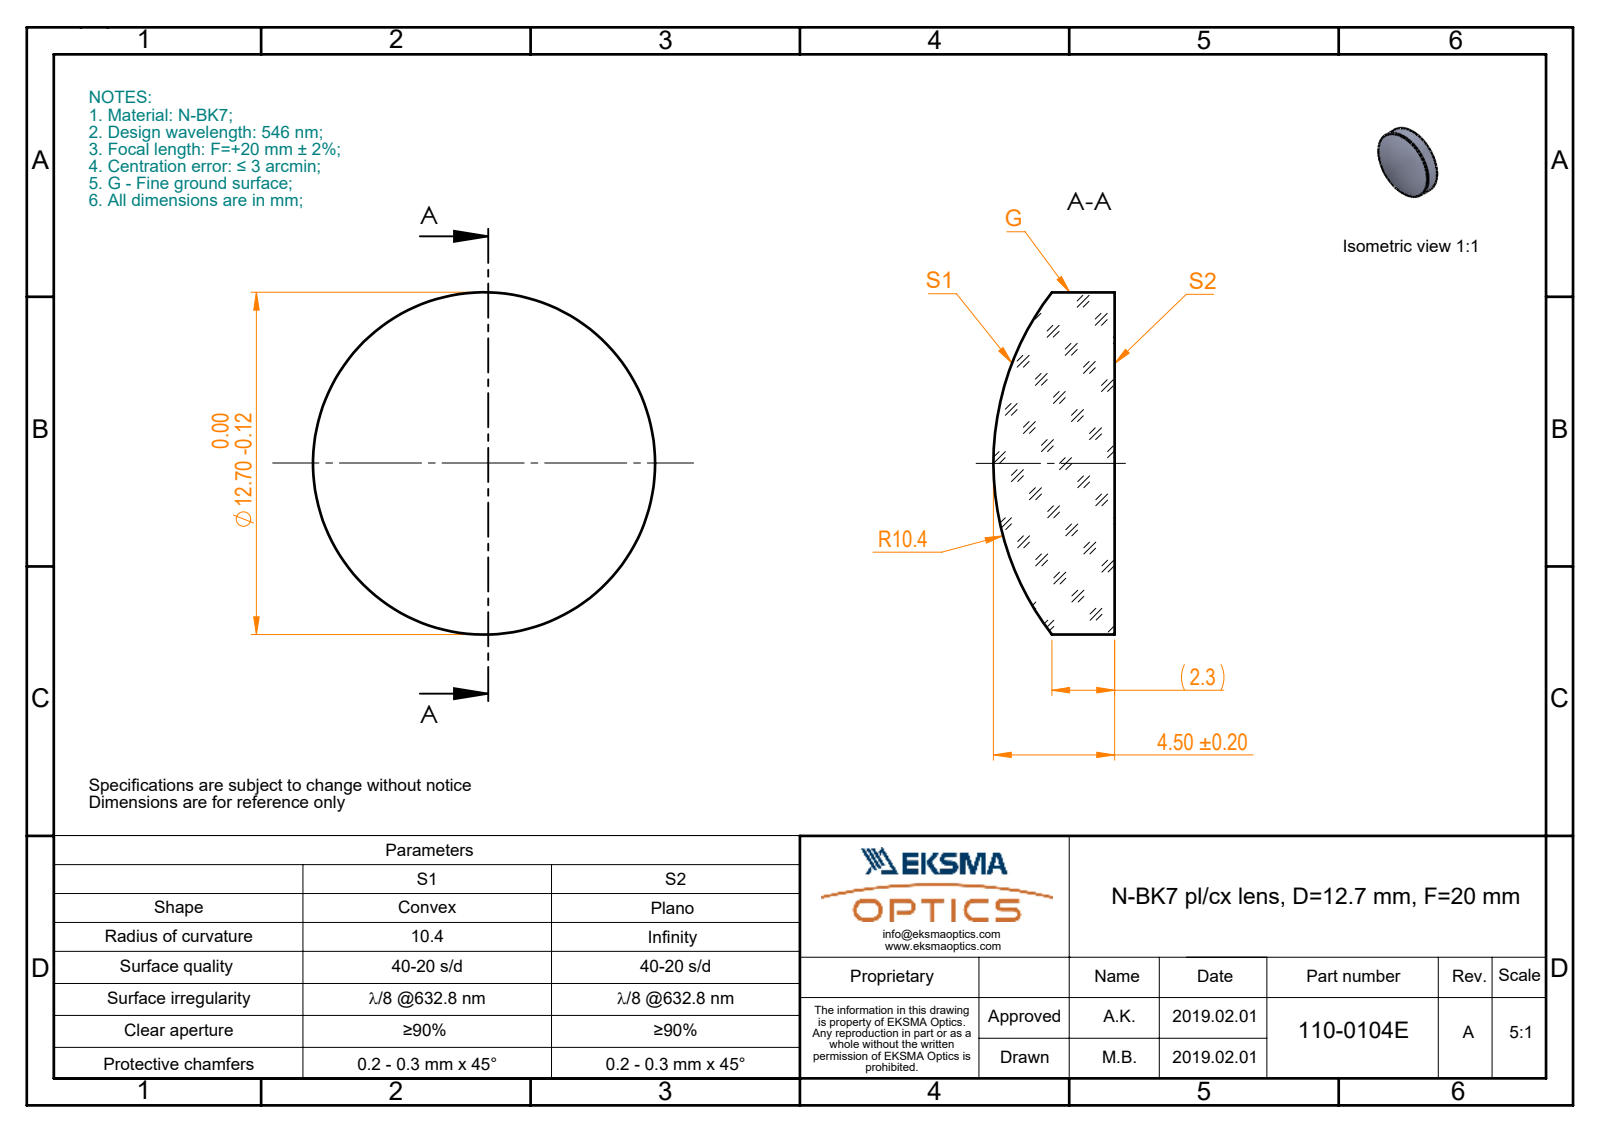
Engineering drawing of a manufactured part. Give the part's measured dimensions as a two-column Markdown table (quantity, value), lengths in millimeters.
| quantity | value |
| --- | --- |
| part name | 110-0104E BK7 pl-cx 12.7 F20 |
| STEP written by | SolidWorks 2017 (CONFIG_CONTROL_DESIGN) |
| units | millimeters |
| bodies | 1 solid, 5 faces (1 planar, 2 cylindrical, 2 other) |
| overall size | 12.7 × 12.7 × 4.5 |
| volume | 438 mm³ |
| surface area | 361 mm² |
| round bosses / shafts (diameter × count) | 12.7 × 1 |
